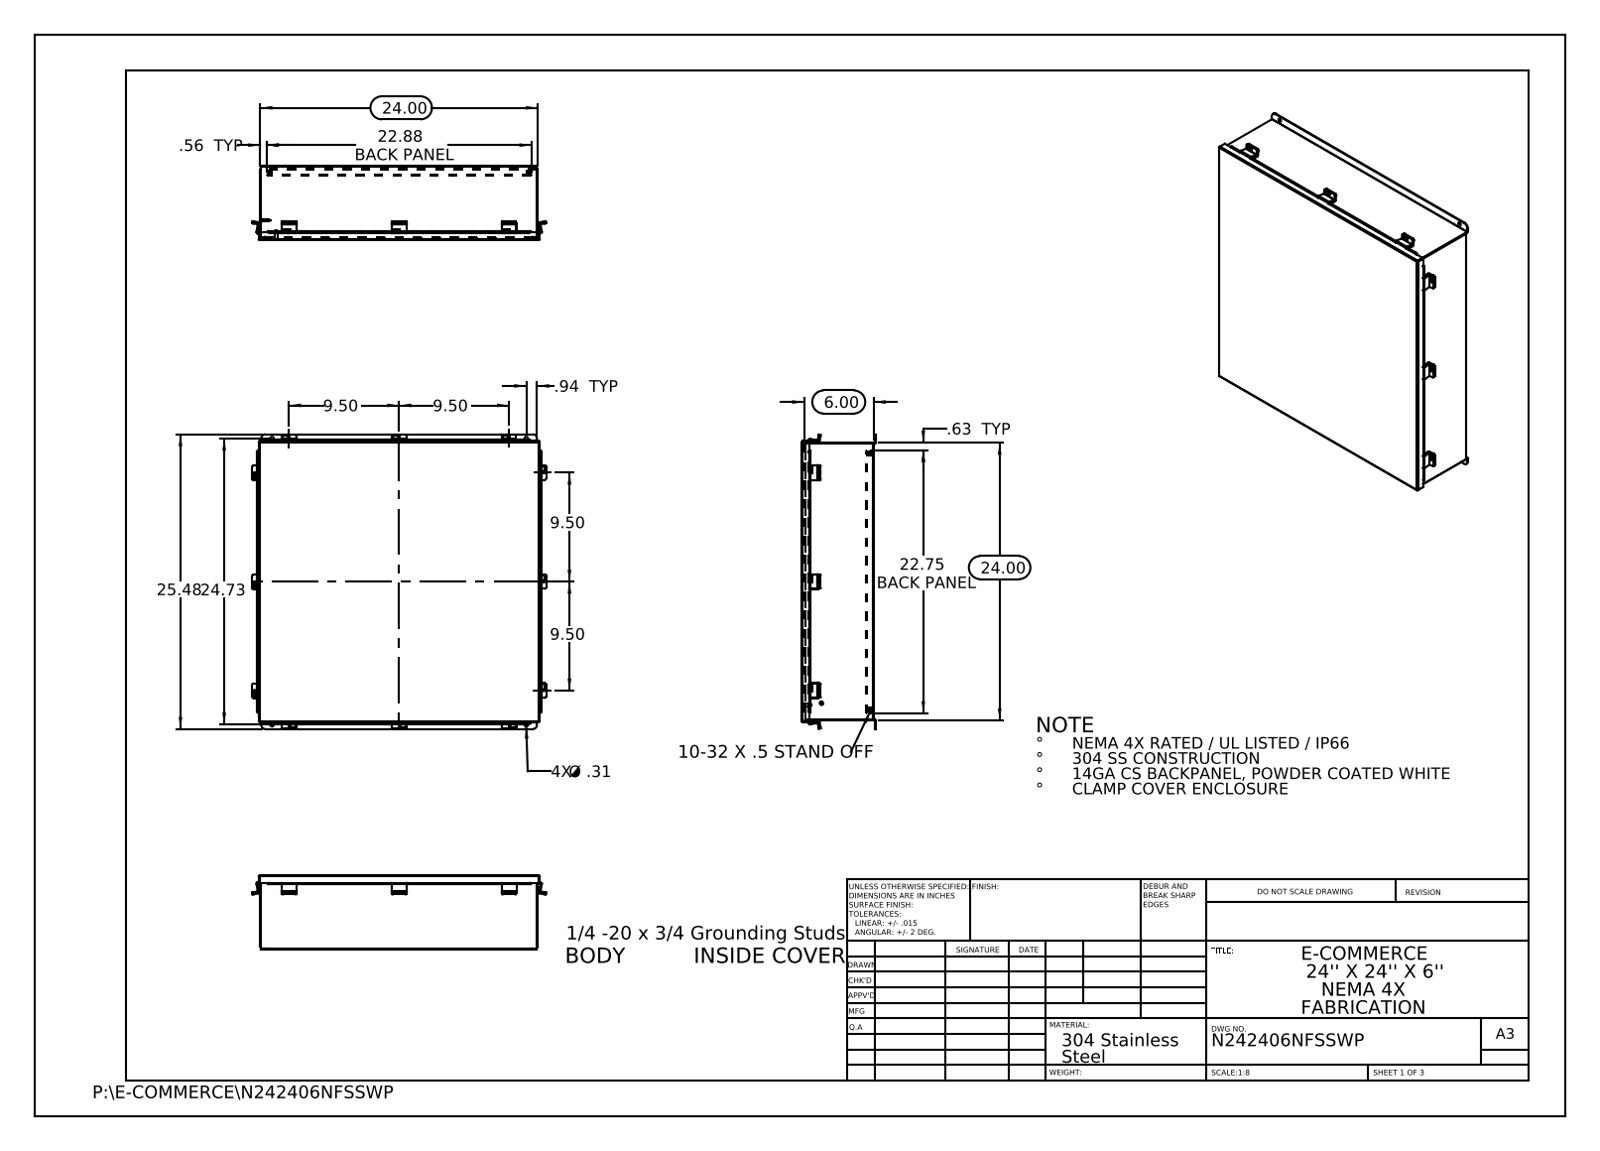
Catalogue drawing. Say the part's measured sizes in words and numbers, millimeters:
The part is named "N242406NFSSWP JIC Top; N242406NFSSWP JIC Bottom; N242406NFSSWP; N242406NFSSWP JIC_Standoff (+6 more)". Its 3-D file was written by "SolidWorks 2013 (CONFIG_CONTROL_DESIGN)". It is 35 solids with 824 faces: 548 planar, 256 cylindrical and 20 other. Overall it measures 647.1 by 645.3 by 162.3 millimeters. Its volume is 2 984 000 cubic millimeters and its surface area 3 167 000 square millimeters. Round holes: 16 of diameter 6.4, 4 of diameter 4.7, 4 of diameter 7.9. Round bosses or shafts: 4 of diameter 8, 2 of diameter 8, 2 of diameter 6. Partial cylindrical surfaces (rounded edges, fillets, slot ends): 42 of radius 3.2, 24 of radius 3.4, 16 of radius 0.2, 12 of radius 0.3, 12 of radius 2.2, 8 of radius 2.1, 8 of radius 2.5, 4 of radius 2.1. The main face-to-face distances are 1.9, 155.7, 607.7, 153.7, 157.6, 1.9, 143, 14.6, 12.7, 141. The hole center spacings are 33.4, 239.4, 241.3, 564.2, 595, 819.3, 478.8, 482.6.
